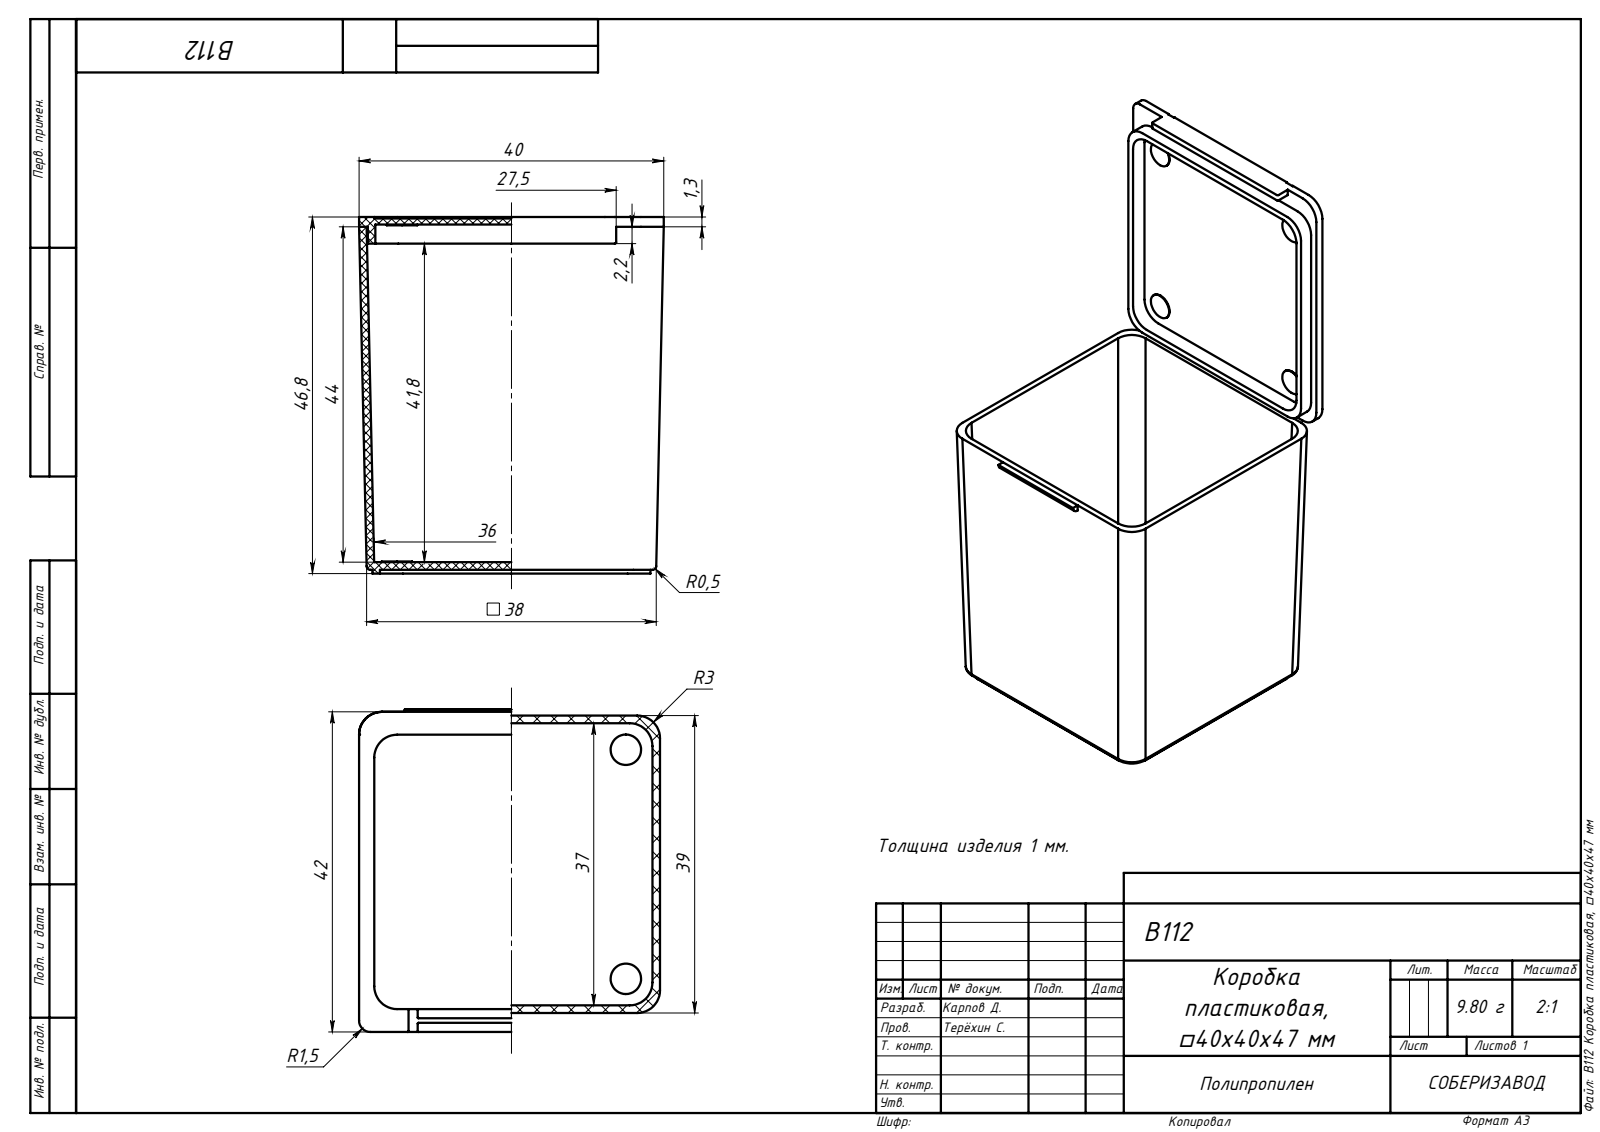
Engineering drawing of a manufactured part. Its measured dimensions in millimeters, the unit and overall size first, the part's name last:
Units: millimetres
Overall size (bounding box): 46.79 × 42.3 × 40
Round bosses / shafts (diameter × count): ⌀4 ×8
Partial cylindrical surfaces — rounded edges, fillets, slot ends (radius × count): R3 ×31, R0.1 ×10, R0.5 ×4, R0.2 ×3, R0.3 ×1, R1 ×1, R1.5 ×1
Main face-to-face distances: 1, 45.29, 45.09, 46.09, 0.8, 44.29, 46.29, 1.1, 44.99, 1.3
Volume: 10 140 mm³ · Surface area: 20 526 mm²
Bodies: 3 solids, 152 faces (77 planar, 67 cylindrical, 8 other)
Part name (STEP PRODUCT): B112 Крышка; B112 Коробка пластиковая, ?40x40x47 мм; B112 Емкость
STEP written by: SolidWorks 2020 (AUTOMOTIVE_DESIGN)
